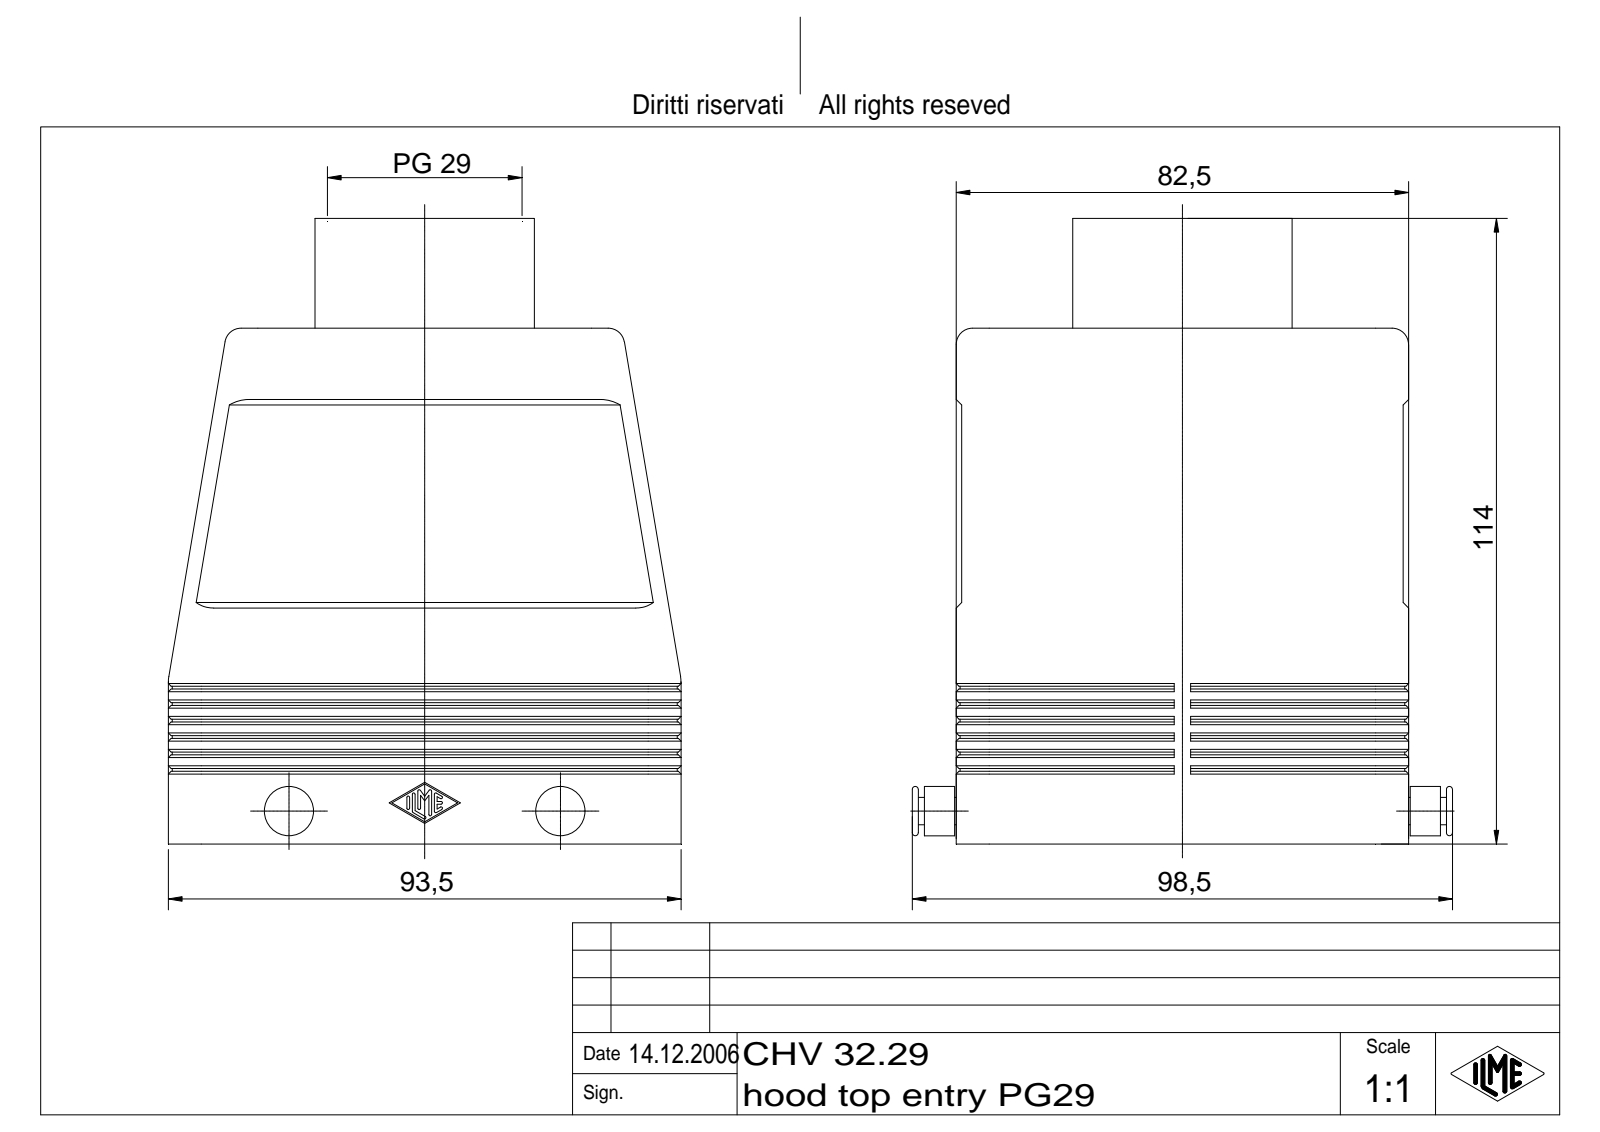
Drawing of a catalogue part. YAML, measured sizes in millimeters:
part_name: "CHV 32.29"
step_written_by: "Autodesk Inventor 7 (AUTOMOTIVE_DESIGN)"
units: millimeters
bodies: {solids: 1, faces: 626, planar: 212, cylindrical: 166, other: 248}
overall_size: [114, 98.5, 93.5]
volume: 158788
surface_area: 80684
round_holes:
  - {diameter: 2.46, count: 4}
  - {diameter: 3.5, count: 4}
  - {diameter: 33.48, count: 1}
  - {diameter: 35.48, count: 1}
  - {diameter: 51, count: 1}
round_bosses_or_shafts:
  - {diameter: 9, count: 2}
  - {diameter: 5, count: 2}
  - {diameter: 65, count: 1}
  - {diameter: 49, count: 1}
  - {diameter: 48, count: 1}
  - {diameter: 40, count: 1}
partial_cylinders:
  - {radius: 0.25, count: 14}
  - {radius: 2, count: 12}
  - {radius: 6, count: 10}
  - {radius: 3, count: 4}
  - {radius: 5.3, count: 2}
face_to_face_distances: [4, 78.5, 74.5, 82.5, 3, 1, 71.5, 11, 77.5, 81.5]
hole_center_spacings: [27, 38.96, 49.62, 77.5, 82.07]
